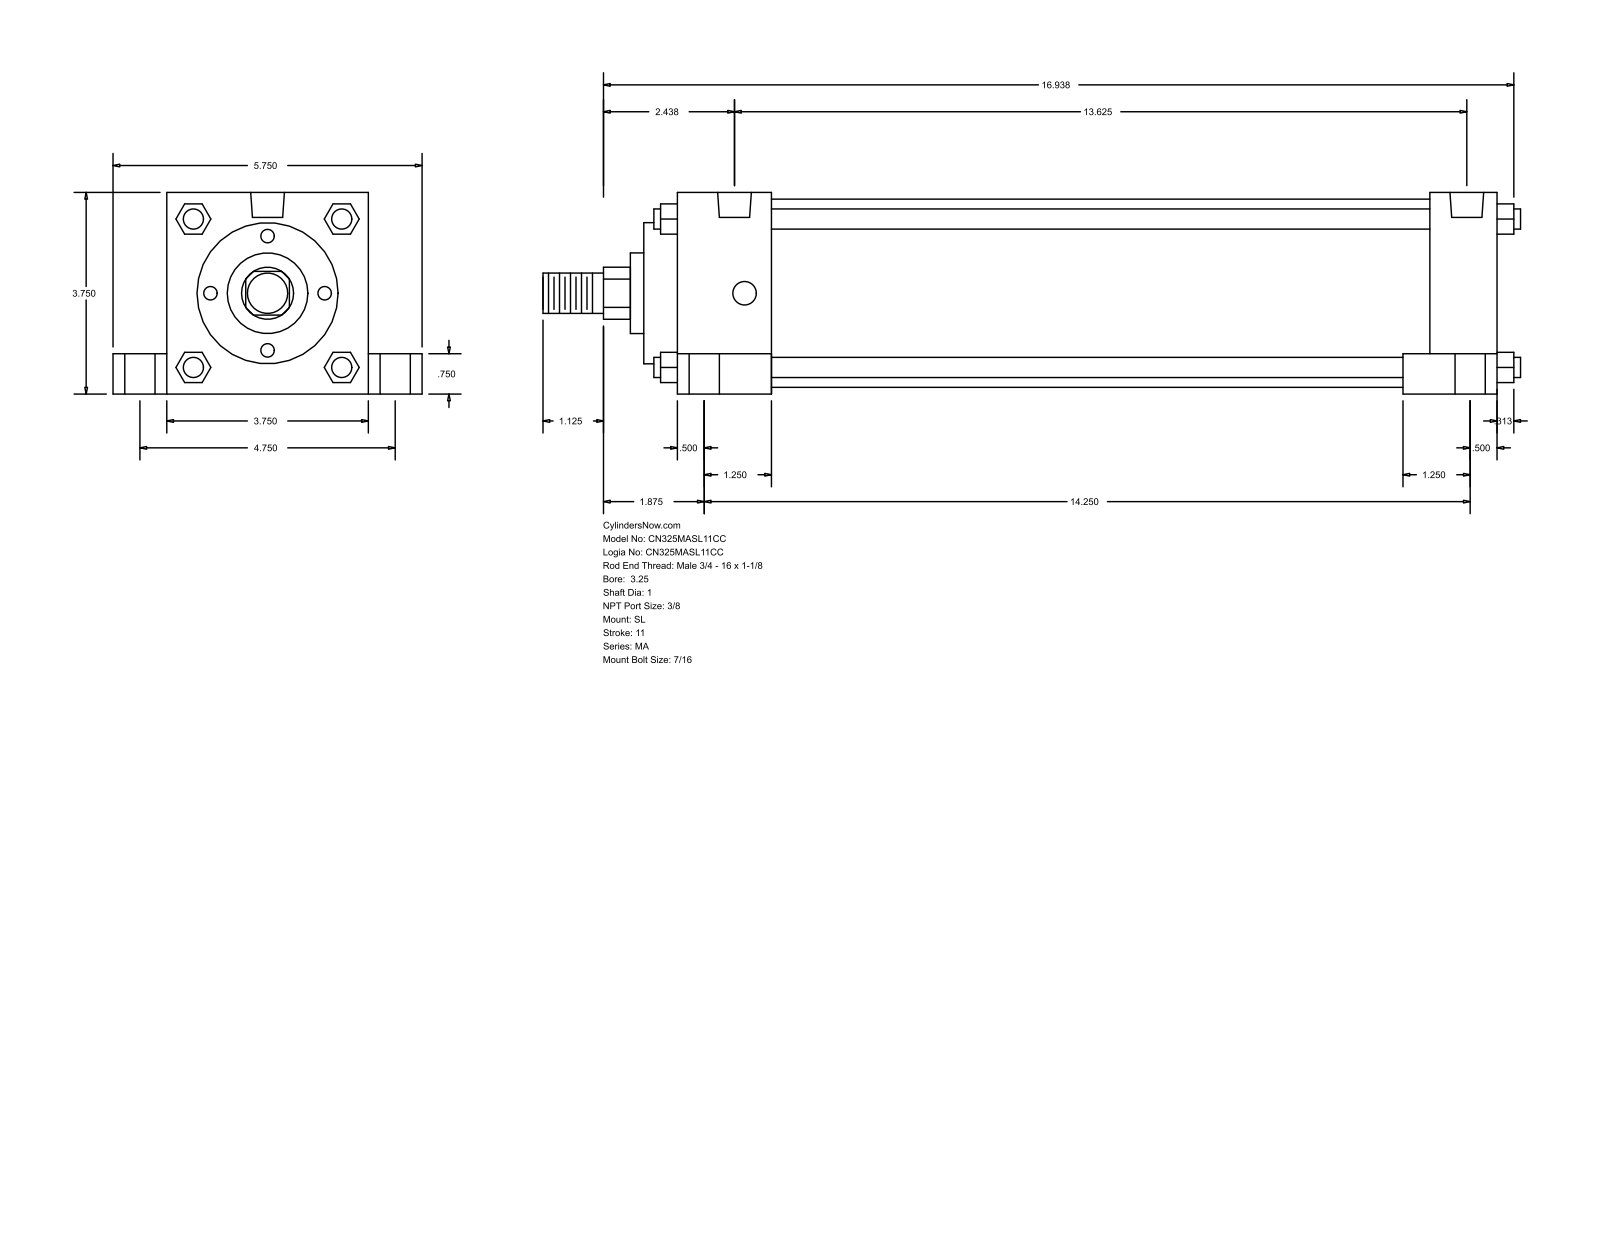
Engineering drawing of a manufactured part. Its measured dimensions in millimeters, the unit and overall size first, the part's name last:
Units: millimetres
Overall size (bounding box): 461.96 × 146.05 × 95.25
Round holes (diameter × count): ⌀11.11 ×4, ⌀14.29 ×4, ⌀20.64 ×4, ⌀15.93 ×2
Round bosses / shafts (diameter × count): ⌀9.53 ×4, ⌀88.9 ×1, ⌀66.67 ×1, ⌀38.1 ×1, ⌀25.4 ×1, ⌀19.05 ×1
Partial cylindrical surfaces — rounded edges, fillets, slot ends (radius × count): R12.29 ×1
Main face-to-face distances: 95.24, 387.35, 15.87, 25.41, 120.65, 403.22, 19.05, 355.6, 31.75, 44.46
Hole centre spacings: 4.76, 60.35, 60.66, 62, 63.27, 120.66, 336.56, 341.32
Bodies: 0 solids, 150 faces (113 planar, 37 cylindrical, 0 other)
Part name (STEP PRODUCT): MA_SL__0325_1
STEP written by: GSSL Pune (CONFIG_CONTROL_DESIGN)
